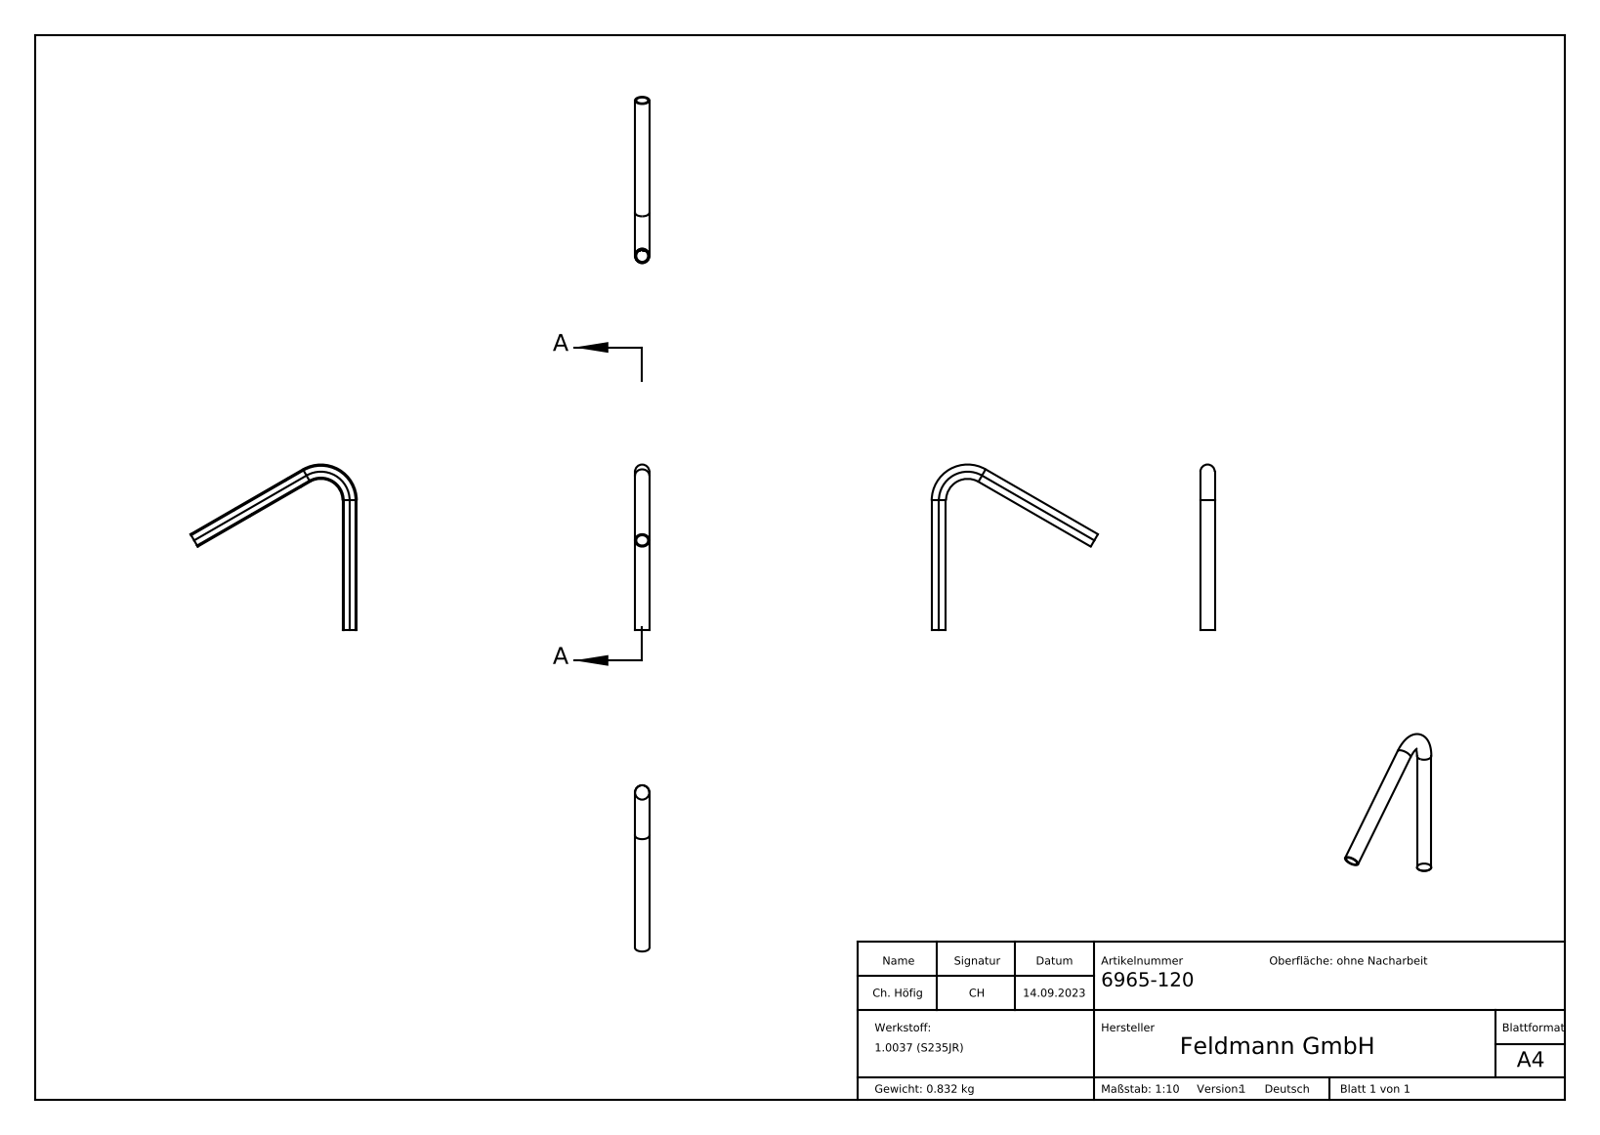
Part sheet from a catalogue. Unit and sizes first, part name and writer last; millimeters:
Units: millimetres
Overall size (bounding box): 312.01 × 310.9 × 26.9
Round holes (diameter × count): ⌀22.3 ×2
Round bosses / shafts (diameter × count): ⌀26.9 ×2
Main face-to-face distances: 0.53, 0.58, 0.34, 0.39, 0.32, 0.48, 0.31, 0.35, 0.4, 0.54
Volume: 106 651 mm³ · Surface area: 93 099 mm²
Bodies: 1 solid, 214 faces (110 planar, 4 cylindrical, 100 other)
Part name (STEP PRODUCT): 6965-120
STEP written by: SolidWorks 2018 (CONFIG_CONTROL_DESIGN)
